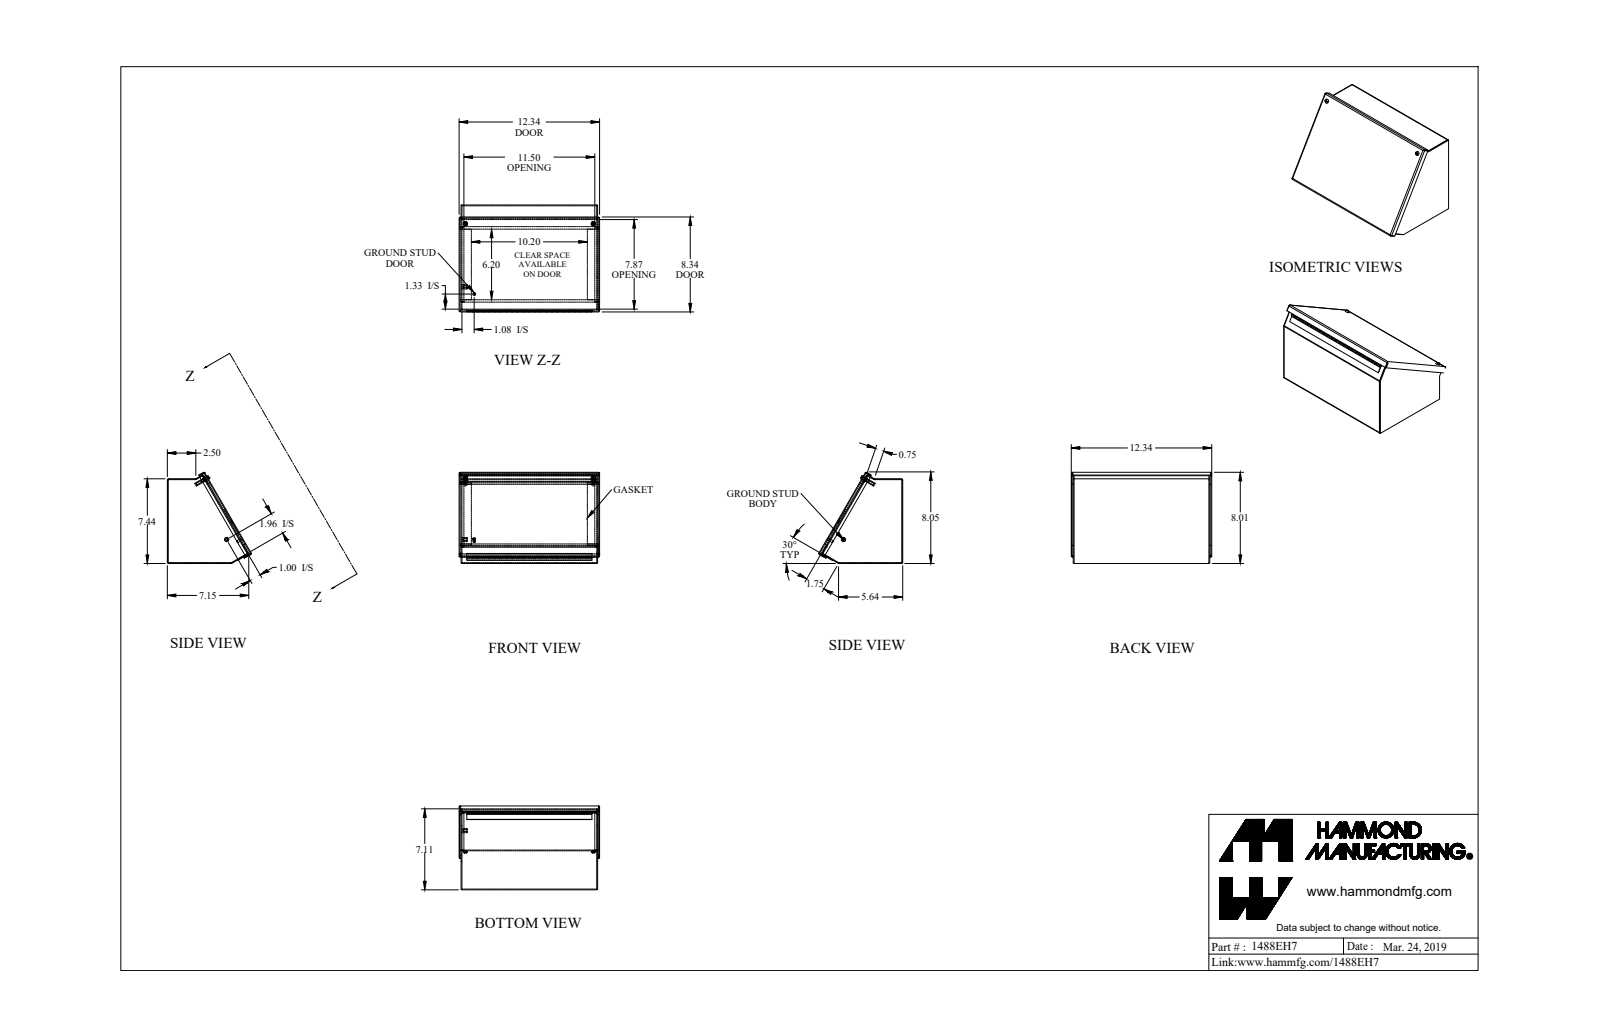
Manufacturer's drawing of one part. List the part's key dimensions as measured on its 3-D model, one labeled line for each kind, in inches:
Part name (STEP PRODUCT): 1488EH7_Default
STEP written by: SolidWorks 2019 (CONFIG_CONTROL_DESIGN)
Units: inches
Bodies: 19 solids, 499 faces (304 planar, 167 cylindrical, 28 other)
Overall size (bounding box): 12.343 × 8.008 × 7.373
Volume: 40.79 in³ · Surface area: 1 003 in²
Round holes (diameter × count): ⌀0.159 ×2, ⌀0.25 ×2, ⌀0.05 ×1, ⌀0.156 ×1
Round bosses / shafts (diameter × count): ⌀0.39 ×2, ⌀0.275 ×2, ⌀0.19 ×2, ⌀0.148 ×2, ⌀0.375 ×1, ⌀0.25 ×1, ⌀0.188 ×1, ⌀0.1 ×1
Partial cylindrical surfaces — rounded edges, fillets, slot ends (radius × count): R0.036 ×12, R0.108 ×12, R0.125 ×2, R0.16 ×2, R0.171 ×2, R0.055 ×1, R0.057 ×1
Main face-to-face distances: 0.072, 0.072, 11.928, 7.365, 11.856, 12, 0.25, 0.322, 7.437, 7.293
Hole centre spacings: 11.25, 11.25, 2.225
